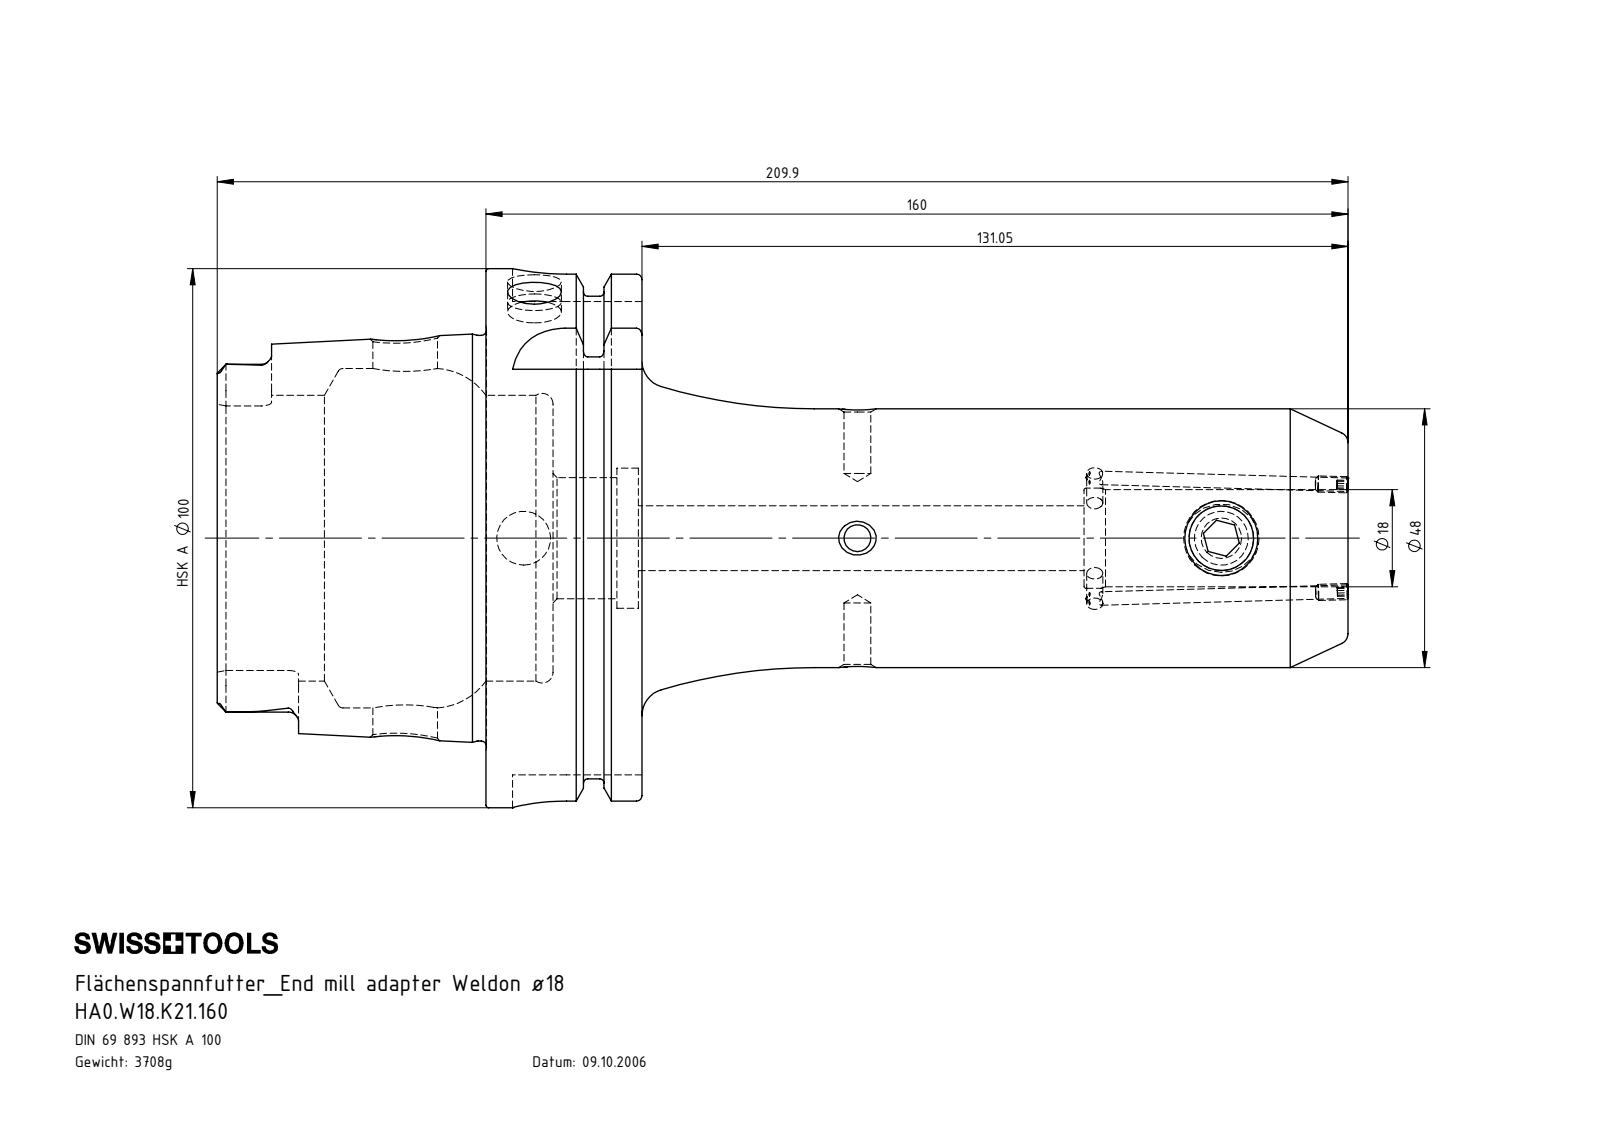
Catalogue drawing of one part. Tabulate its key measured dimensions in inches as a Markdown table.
| quantity | value |
| --- | --- |
| part name | ERU-CJ2.001.006_Default; W16-ER1.001.016_Default; HA0.W18.K21.160; HA0-W18.K21.160_C_Fertigbearbeitung |
| STEP written by | SolidWorks 2009 (CONFIG_CONTROL_DESIGN) |
| units | inches |
| bodies | 4 solids, 273 faces (71 planar, 82 cylindrical, 120 other) |
| overall size | 8.267 × 3.937 × 3.937 |
| volume | 28.82 in³ |
| surface area | 119.7 in² |
| round holes (diameter × count) | 0.394 × 3, 0.472 × 3, 0.098 × 2, 0.197 × 2, 0.118 × 1, 0.709 × 1, 0.732 × 1, 0.886 × 1, 1.024 × 1, 2.087 × 1, 2.48 × 1 |
| round bosses / shafts (diameter × count) | 0.118 × 2, 3.937 × 1, 3.62 × 1, 2.963 × 1, 1.89 × 1, 0.551 × 1 |
| partial cylindrical surfaces (radius × count) | 0.075 × 6, 0.192 × 4, 0.394 × 4 |
| main face-to-face distances | 1.14, 0.65, 0.49, 1.965, 2.455, 3.104, 8.264, 6.299, 5.809, 5.159 |
| hole center spacings | 2.439, 2.659, 3.305, 5.098 |
